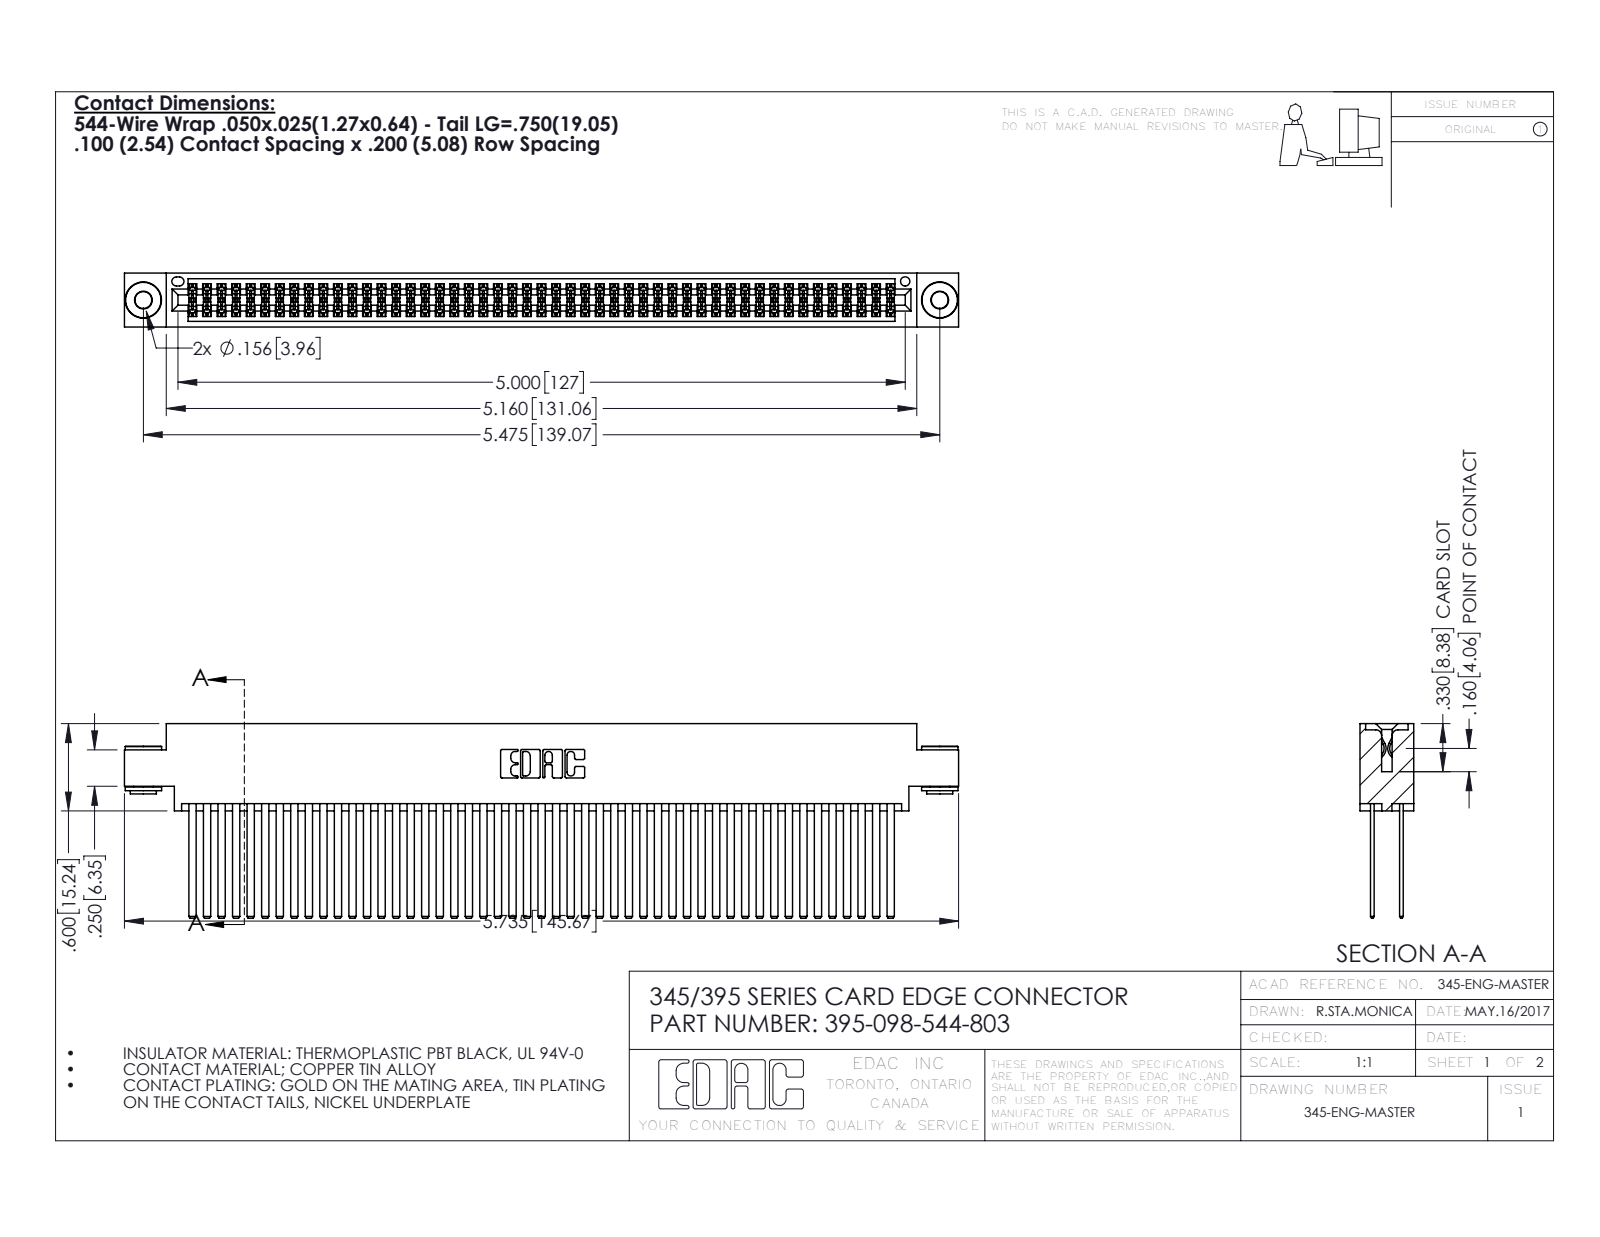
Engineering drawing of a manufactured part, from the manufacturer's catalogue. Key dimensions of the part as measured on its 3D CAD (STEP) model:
Part name (STEP PRODUCT): 345-250-002_345-250-002-102; 345 Part_0.170 Offset - 0.156 Dia-TH; 345-292-001_345-293-144; 395-098-544-803
STEP written by: SolidWorks 2016 (CONFIG_CONTROL_DESIGN)
Units: inches
Bodies: 101 solids, 4480 faces (2936 planar, 1536 cylindrical, 8 other)
Overall size (bounding box): 5.735 × 1.337 × 0.37
Volume: 0.946 in³ · Surface area: 42.49 in²
Round holes (diameter × count): ⌀0.116 ×2, ⌀0.156 ×2, ⌀0.064 ×1
Round bosses / shafts (diameter × count): ⌀0.25 ×2, ⌀0.18 ×2, ⌀0.136 ×2
Partial cylindrical surfaces — rounded edges, fillets, slot ends (radius × count): R0.006 ×147, R0.01 ×22, R0.007 ×6, R0.031 ×6, R0.026 ×3, R0.014 ×2, R0.019 ×2, R0.022 ×2
Main face-to-face distances: 0.2, 0.025, 0.072, 0.098, 0.272, 0.298, 0.225, 0.175, 0.37, 0.15
Hole centre spacings: 0.27, 5.239, 5.475
